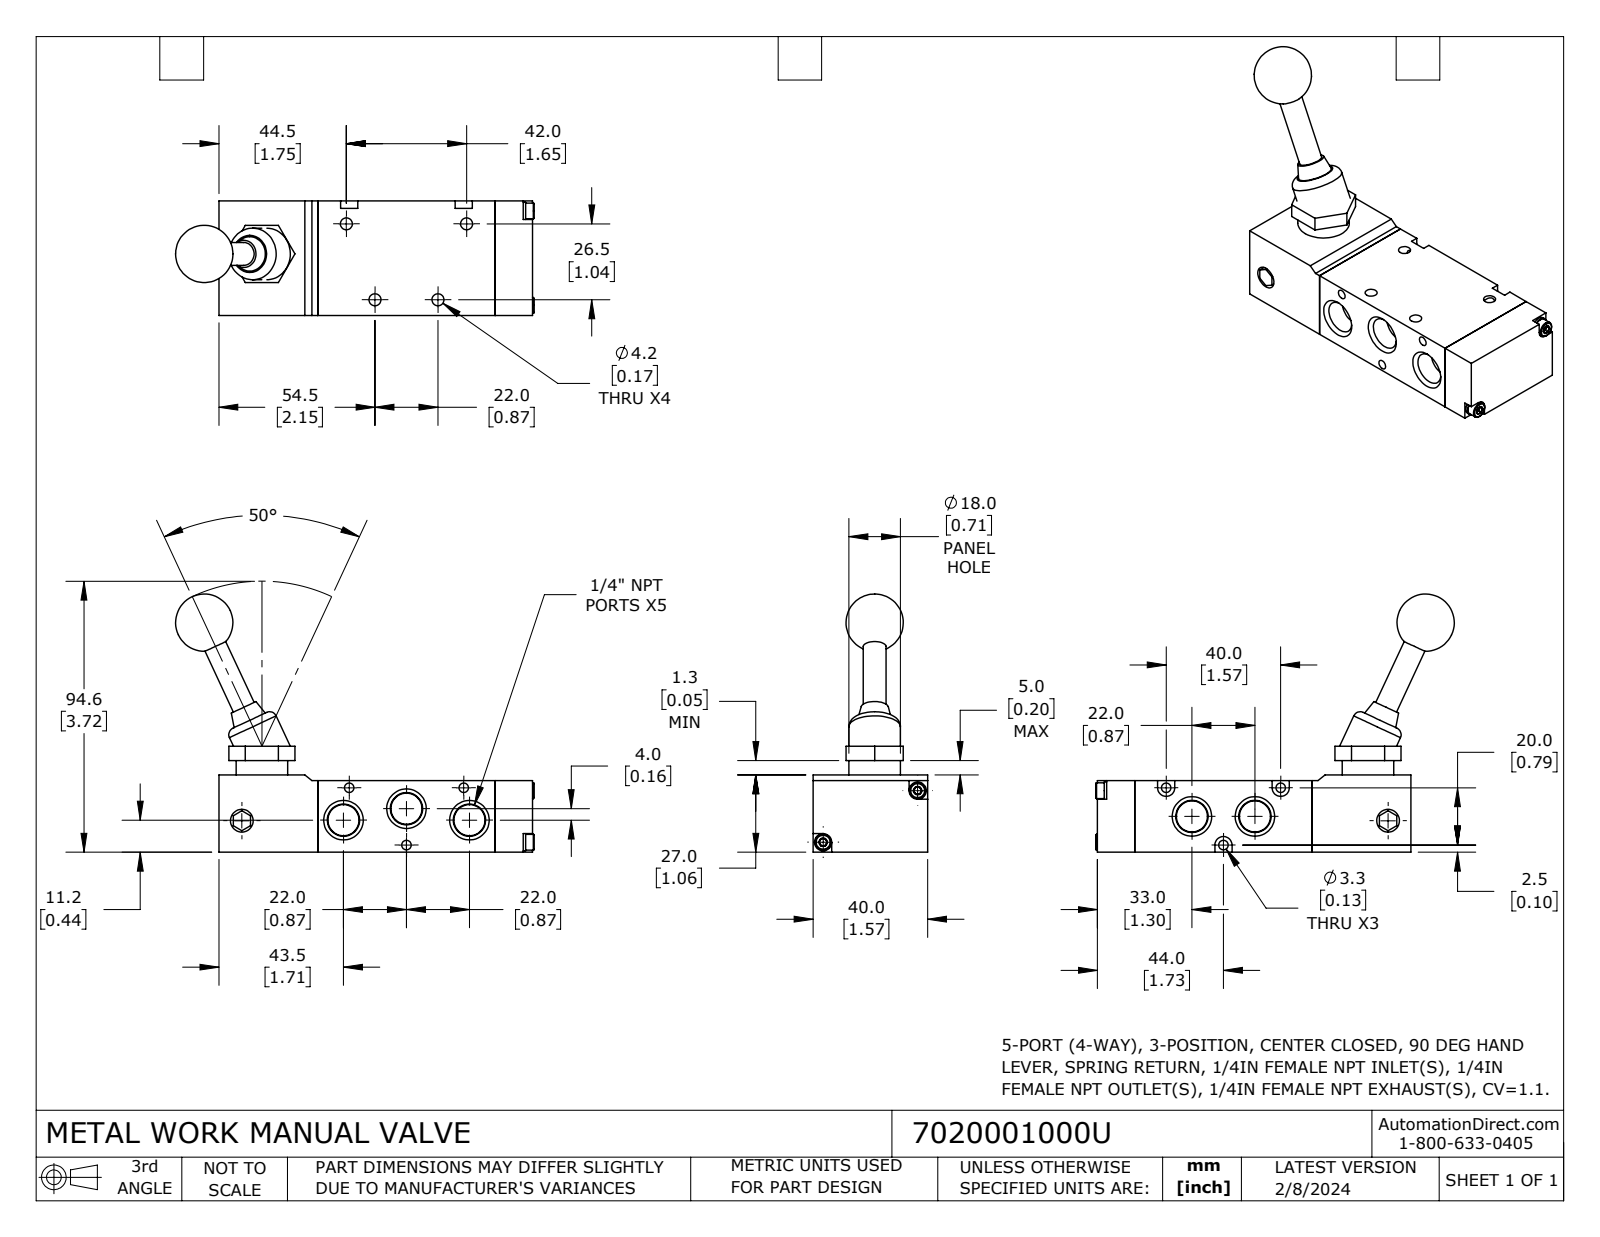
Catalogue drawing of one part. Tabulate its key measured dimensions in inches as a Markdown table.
| quantity | value |
| --- | --- |
| part name | 7020001000U |
| STEP written by | SolidWorks 2023 (CONFIG_CONTROL_DESIGN) |
| units | inches |
| bodies | 8 solids, 206 faces (101 planar, 51 cylindrical, 54 other) |
| overall size | 4.93 × 3.549 × 1.575 |
| volume | 7.193 in³ |
| surface area | 44.53 in² |
| round holes (diameter × count) | 0.165 × 4, 0.13 × 3, 0.118 × 2, 0.313 × 1 |
| round bosses / shafts (diameter × count) | 0.709 × 2, 0.236 × 2, 0.217 × 2, 0.315 × 1 |
| partial cylindrical surfaces (radius × count) | 0.118 × 3 |
| main face-to-face distances | 0.984, 1.575, 2.441, 3.799, 1.358, 1.063, 0.079, 0.512, 2.953, 4.311 |
| hole center spacings | 1.113, 1.115, 1.636, 0.866, 1.48, 1.544, 1.575, 1.654 |
